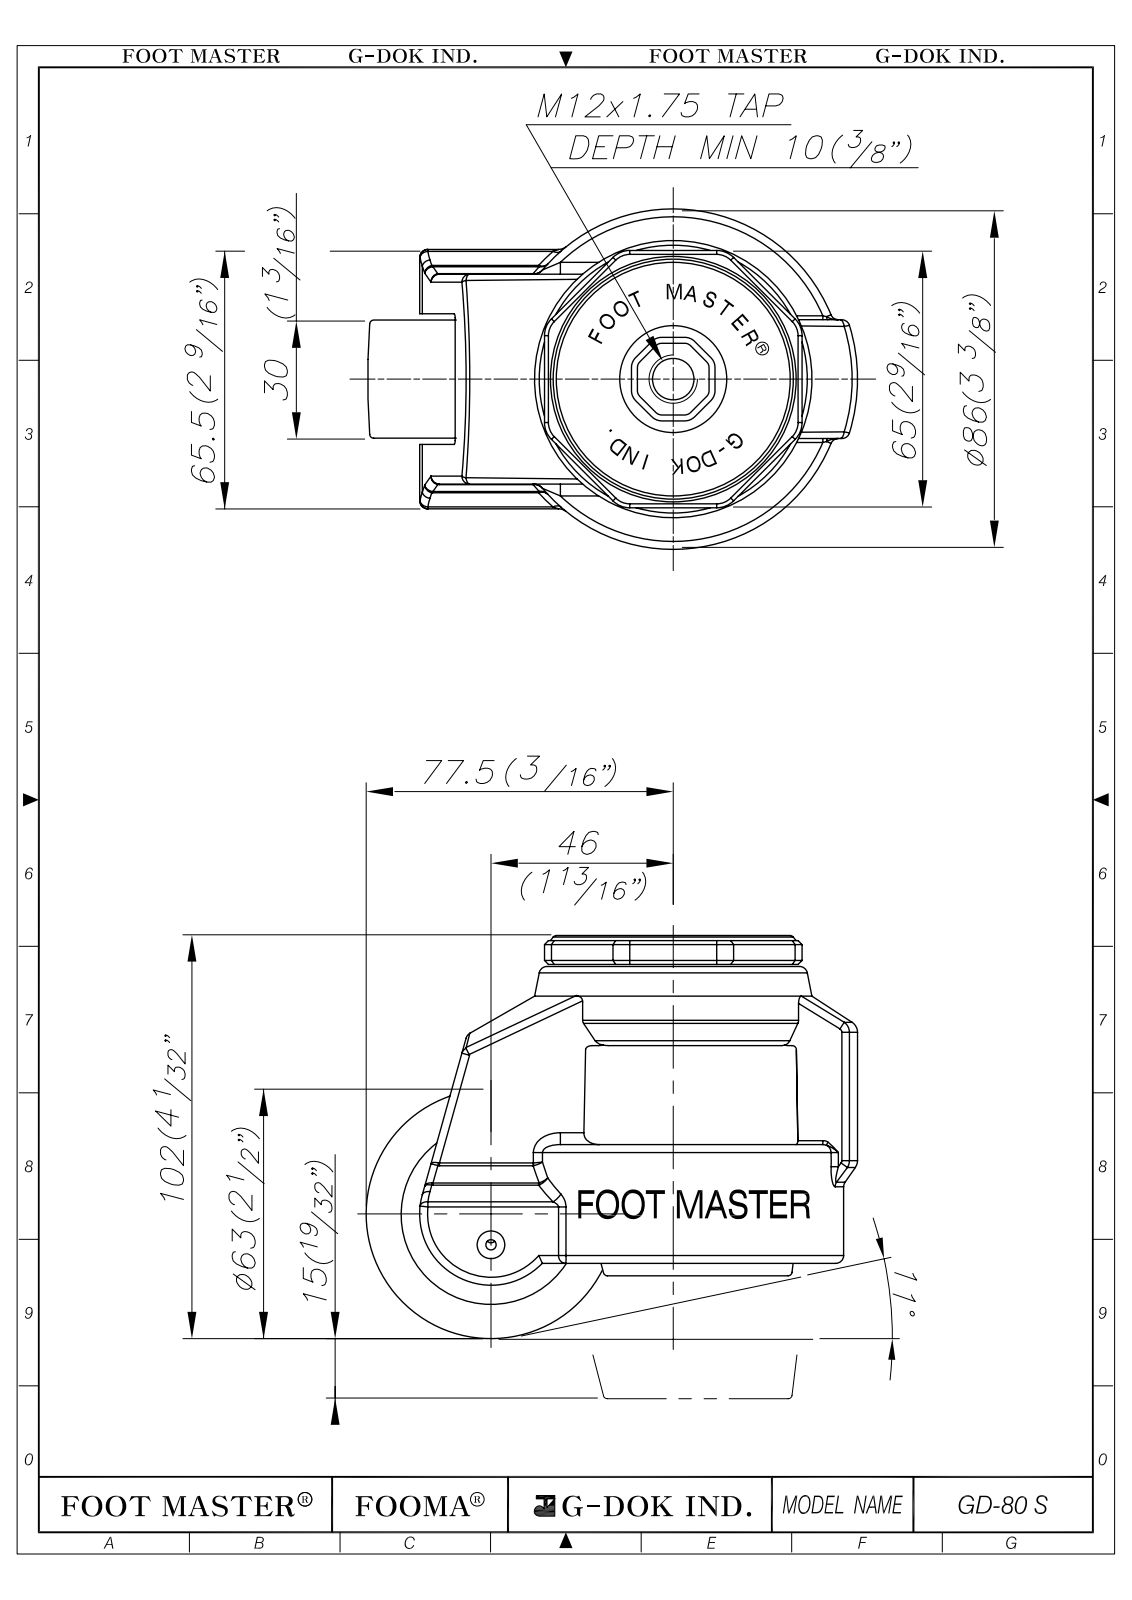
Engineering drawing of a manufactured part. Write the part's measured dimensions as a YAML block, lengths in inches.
part_name: "GD-80S"
step_written_by: "Autodesk Inventor 2009 (AUTOMOTIVE_DESIGN)"
units: inches
bodies: {solids: 4, faces: 1305, planar: 390, cylindrical: 280, other: 635}
overall_size: [4.882, 4.02, 3.386]
volume: 24.68
surface_area: 152.4
round_holes:
  - {diameter: 0.276, count: 2}
  - {diameter: 0.335, count: 1}
  - {diameter: 0.476, count: 1}
  - {diameter: 0.559, count: 1}
  - {diameter: 0.591, count: 1}
  - {diameter: 1.102, count: 1}
  - {diameter: 1.614, count: 1}
  - {diameter: 1.772, count: 1}
round_bosses_or_shafts:
  - {diameter: 0.472, count: 2}
  - {diameter: 0.118, count: 2}
  - {diameter: 2.756, count: 1}
  - {diameter: 2.48, count: 1}
  - {diameter: 1.535, count: 1}
  - {diameter: 1.063, count: 1}
  - {diameter: 0.787, count: 1}
  - {diameter: 0.394, count: 1}
partial_cylinders:
  - {radius: 0.079, count: 76}
  - {radius: 0.02, count: 40}
  - {radius: 0.039, count: 32}
  - {radius: 0.197, count: 9}
  - {radius: 0.118, count: 4}
  - {radius: 0.075, count: 1}
  - {radius: 0.138, count: 1}
  - {radius: 0.244, count: 1}
face_to_face_distances: [0.433, 0.059, 1.24, 1.673, 1.732, 0.217, 0.374, 1.693, 1.181, 0.039]
hole_center_spacings: [0.071, 0.236, 0.307]
